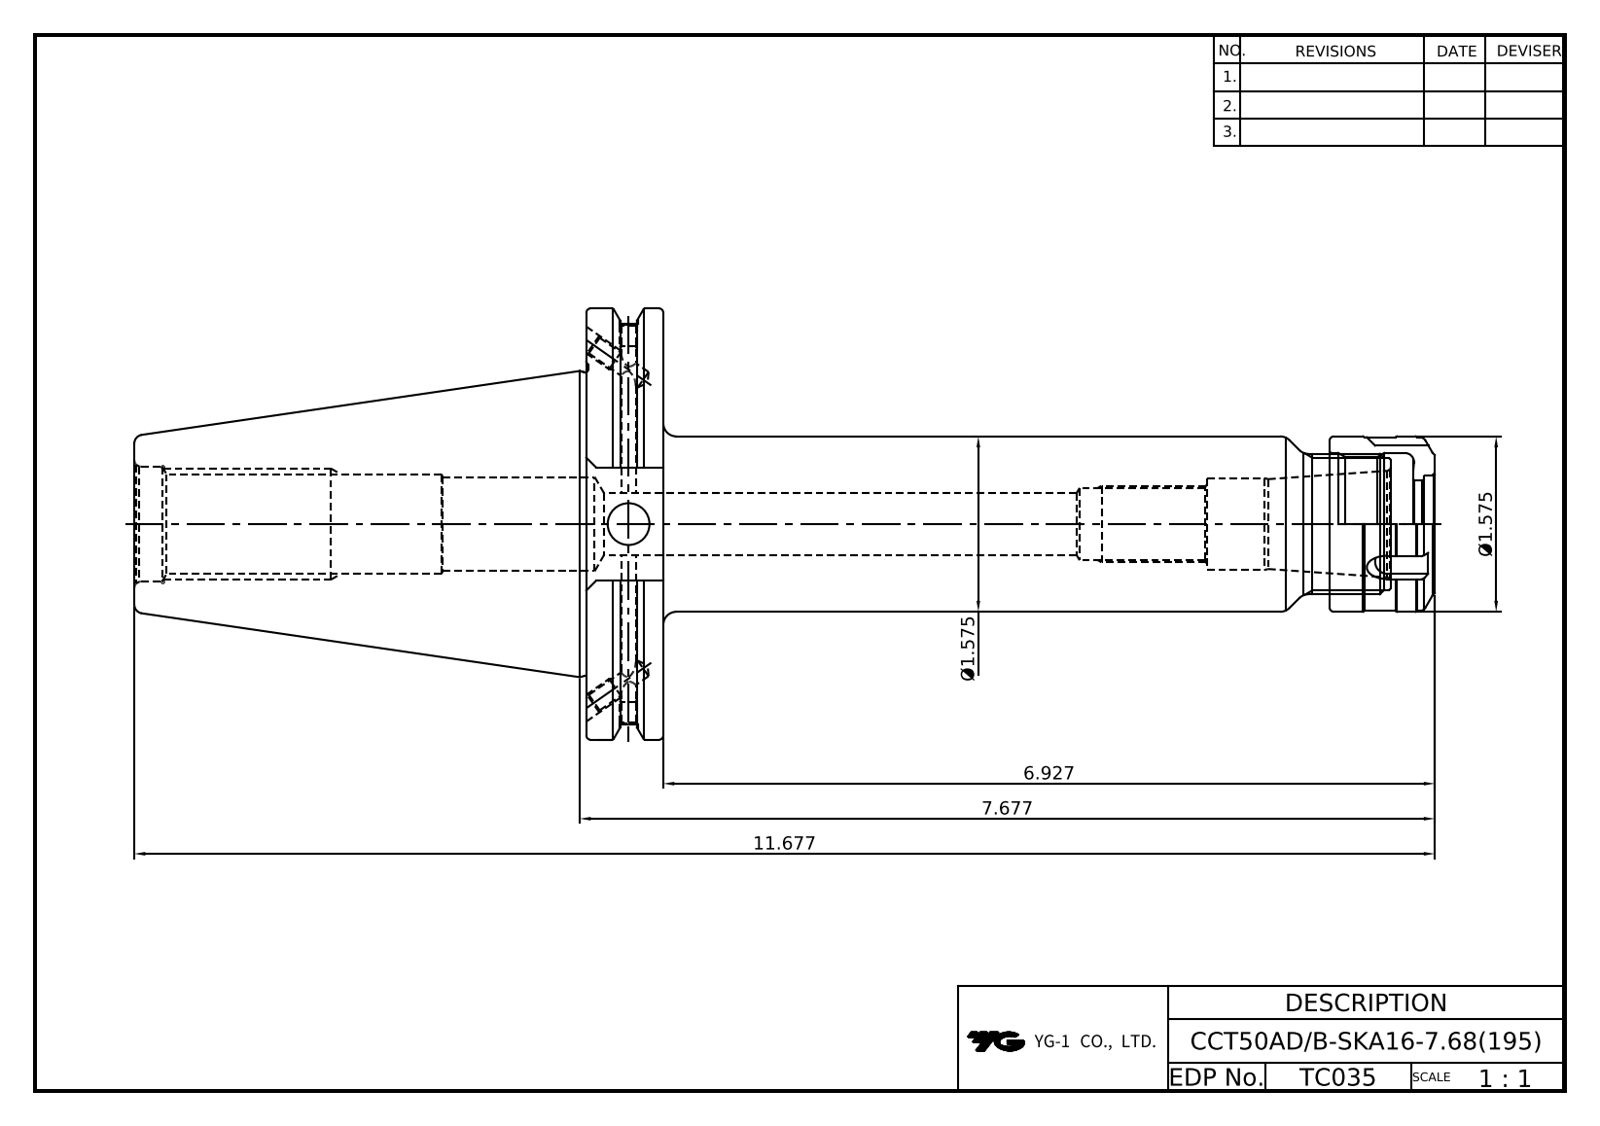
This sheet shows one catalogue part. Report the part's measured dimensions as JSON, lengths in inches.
{"part_name": "LO-CCT50ADB-SKA16-195; SKN16-NUT", "step_written_by": "Autodesk Inventor 2022 (AUTOMOTIVE_DESIGN)", "units": "inches", "bodies": {"solids": 2, "faces": 166, "planar": 59, "cylindrical": 48, "other": 59}, "overall_size": [11.677, 3.875, 3.728], "volume_in3": 30.56, "surface_area_in2": 124.3, "round_holes": [[0.128, 2], [0.163, 2], [0.165, 2], [0.197, 2], [0.375, 1], [0.551, 1], [0.62, 1], [0.78, 1], [0.827, 1], [0.846, 1], [0.865, 1], [0.866, 1]], "round_bosses_or_shafts": [[3.875, 1], [3.594, 1], [2.726, 1], [1.575, 1], [1.559, 1], [1.18, 1]], "face_to_face_distances": [0.691, 4.059, 4.75, 11.484, 7.425, 6.734, 11.677, 7.618, 6.927, 0.193]}
